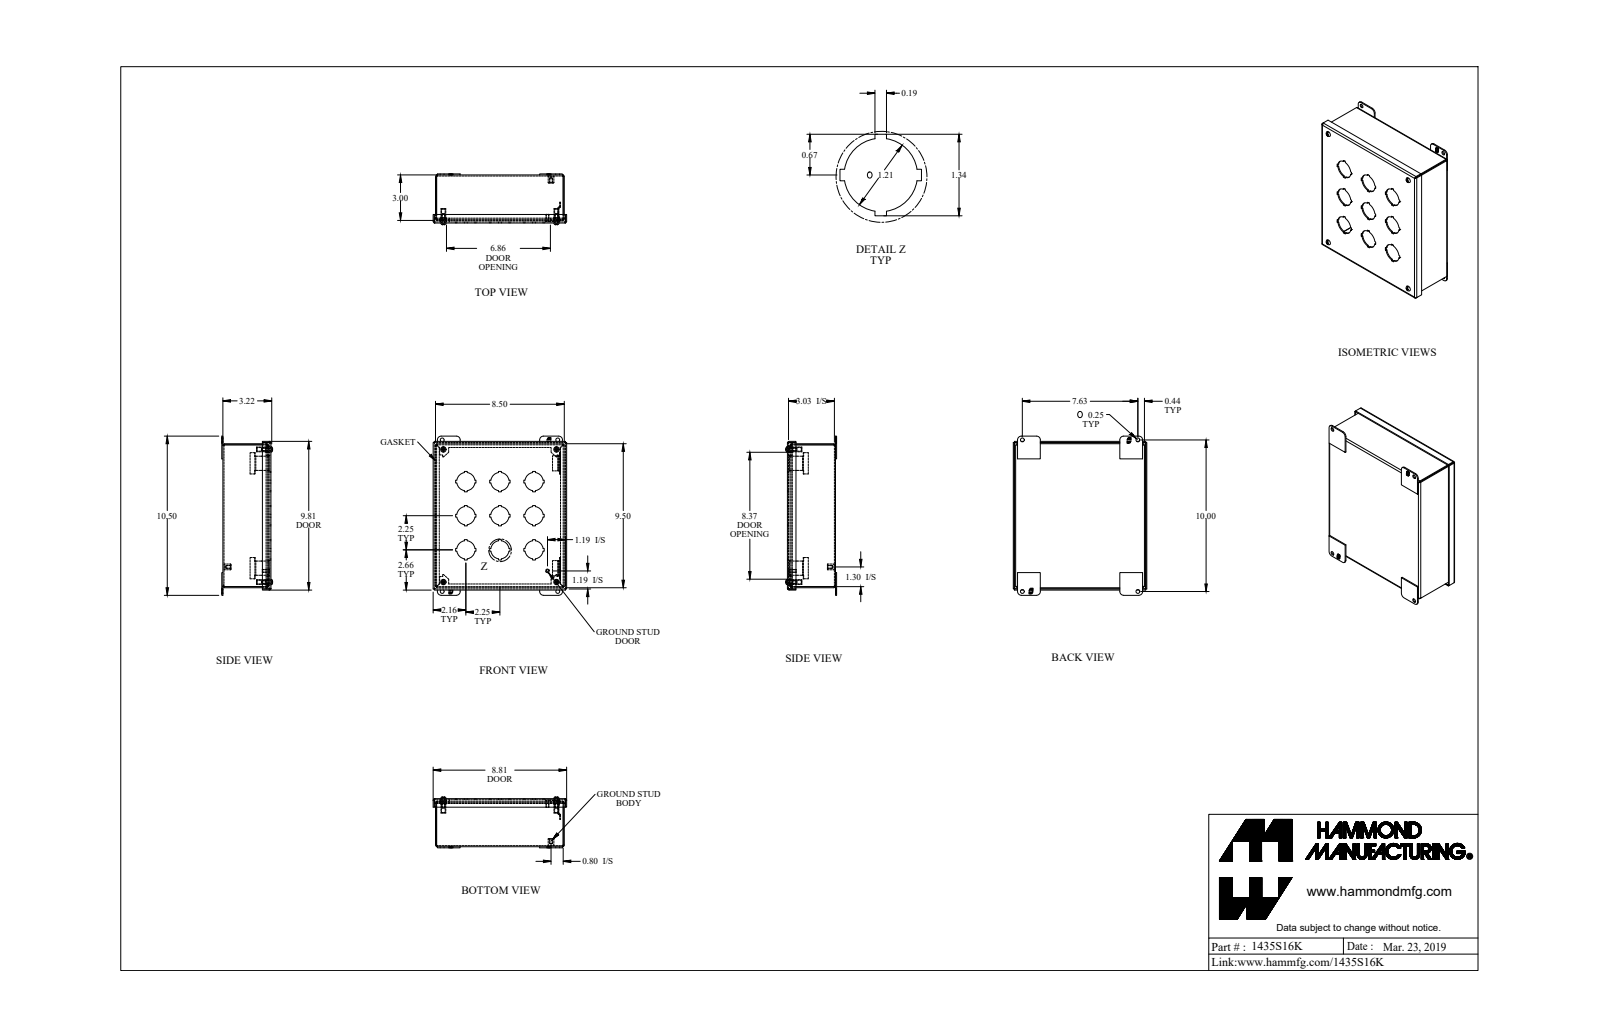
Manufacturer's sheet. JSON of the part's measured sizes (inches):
{"part_name": "1435S16K_Default", "step_written_by": "SolidWorks 2019 (CONFIG_CONTROL_DESIGN)", "units": "inches", "bodies": {"solids": 23, "faces": 749, "planar": 531, "cylindrical": 188, "other": 30}, "overall_size": [10.5, 8.81, 3.354], "volume_in3": 24.81, "surface_area_in2": 658.8, "round_holes": [[1.21, 9], [0.25, 8], [0.065, 4], [0.239, 4], [0.253, 4], [0.406, 4], [0.156, 1]], "round_bosses_or_shafts": [[0.19, 5], [0.406, 4], [0.315, 4], [0.148, 4], [0.375, 1], [0.25, 1]], "partial_cylinders_radius": [[0.036, 12], [0.108, 12], [0.25, 8], [0.029, 4], [0.086, 4], [0.171, 4]], "face_to_face_distances": [0.072, 3.1, 3.172, 3.028, 8.428, 9.428, 0.155, 8.5, 8.356, 9.5], "hole_center_spacings": [2.25, 3.182, 5.031, 7.46, 7.461, 7.569, 8.749, 8.75]}
